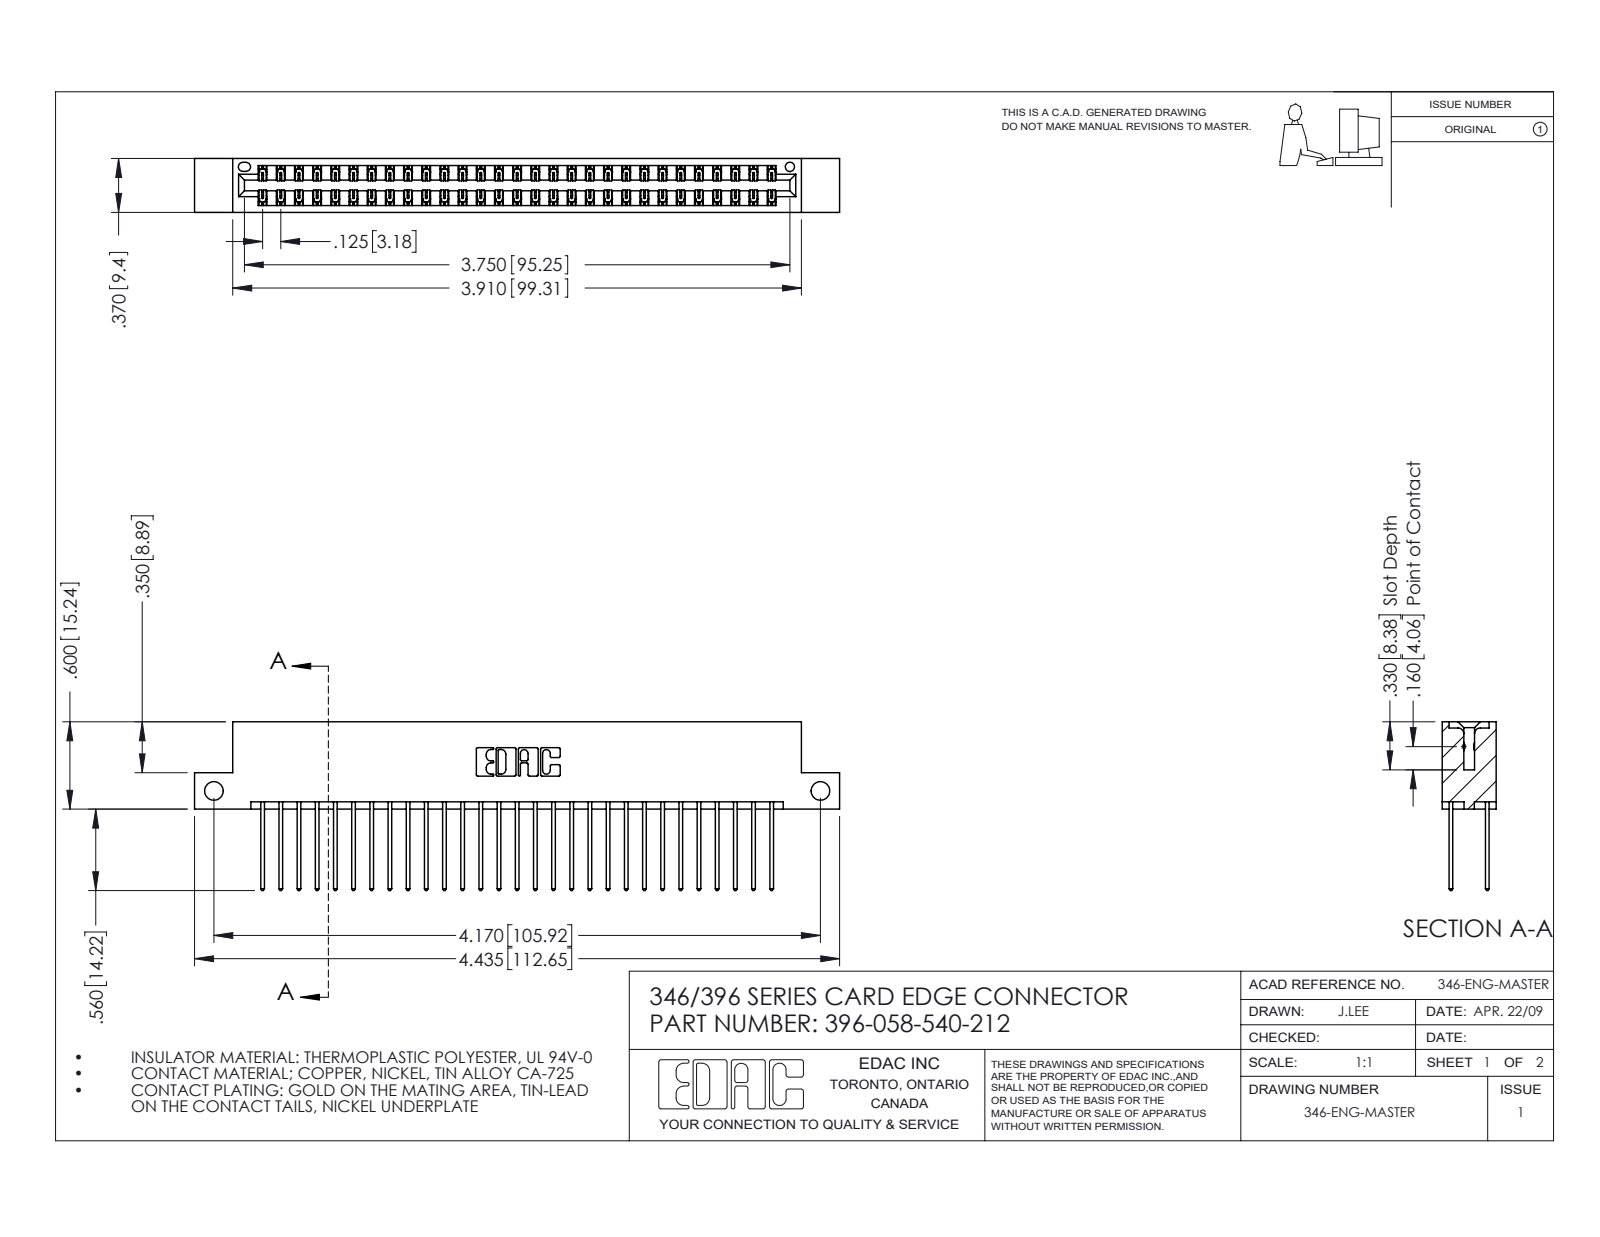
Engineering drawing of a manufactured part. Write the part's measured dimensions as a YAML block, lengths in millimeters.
part_name: "345-292-001_345-293-140; 396-058-540-212; 346 Part_Flush Mounting Lugs - Side Mount"
step_written_by: "SolidWorks 2016 (CONFIG_CONTROL_DESIGN)"
units: millimeters
bodies: {solids: 59, faces: 3138, planar: 2106, cylindrical: 1032, other: 0}
overall_size: [112.6, 29.5, 9.4]
volume: 11000
surface_area: 15840
round_holes:
  - {diameter: 3.3, count: 2}
  - {diameter: 1.6, count: 1}
partial_cylinders:
  - {radius: 0.2, count: 87}
  - {radius: 0.3, count: 58}
  - {radius: 0.3, count: 22}
  - {radius: 0.2, count: 6}
  - {radius: 0.8, count: 6}
  - {radius: 0.7, count: 3}
  - {radius: 0.4, count: 2}
  - {radius: 0.6, count: 2}
face_to_face_distances: [1.2, 8.2, 6.4, 1.8, 7.6, 0.6, 9.4, 7, 3.8, 5.6]
hole_center_spacings: [105.9]
